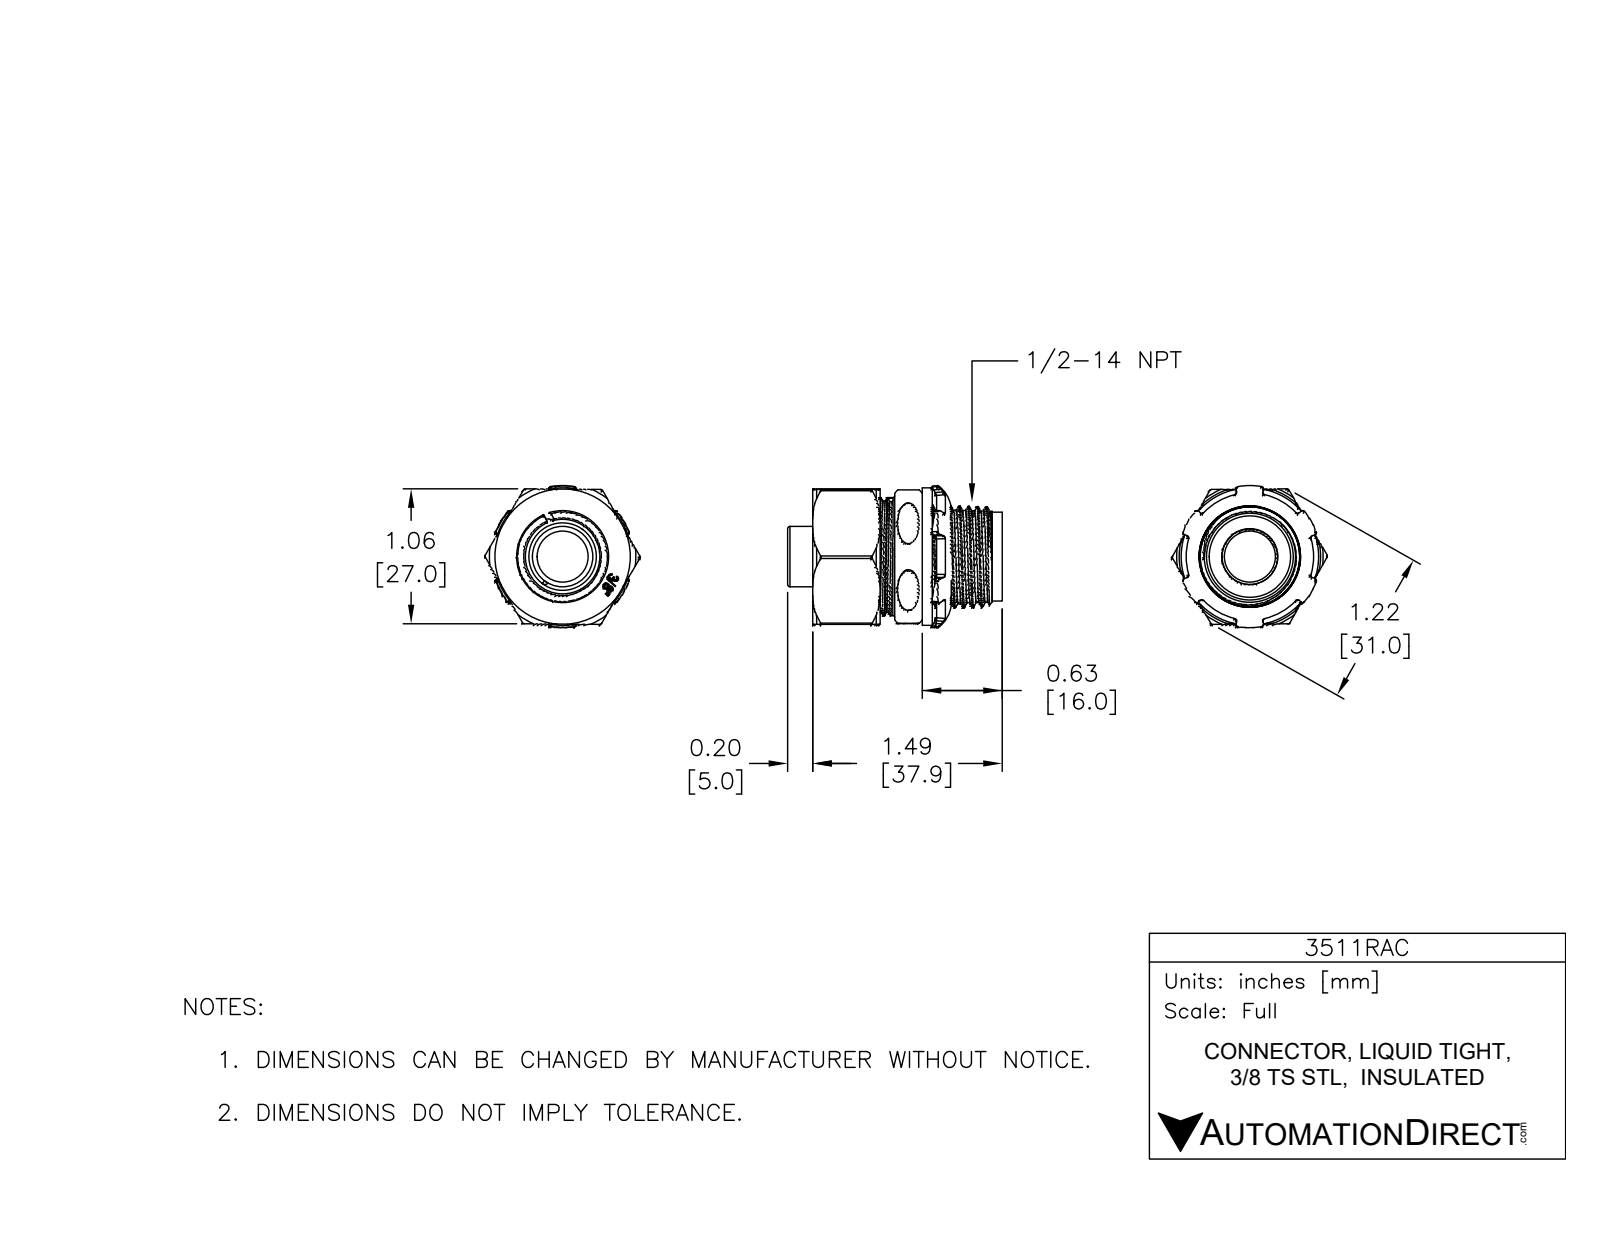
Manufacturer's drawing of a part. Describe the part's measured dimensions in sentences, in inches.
The part is named "3511RAC; 3511RAC-4; 3511RAC-2; 3511RAC-5 (+4 more)". Its 3-D file was written by "SolidWorks 2017 (AUTOMOTIVE_DESIGN)". It is 7 solids with 656 faces: 222 planar, 102 cylindrical and 332 other. Overall it measures 1.695 by 1.221 by 1.119 inches. Its volume is 0.549 cubic inches and its surface area 23.43 square inches. Round holes: 1 of diameter 0.1, 1 of diameter 0.402, 1 of diameter 0.44, 1 of diameter 0.567, 1 of diameter 0.728, 1 of diameter 0.732, 1 of diameter 0.787, 1 of diameter 0.858, 1 of diameter 0.906. Round bosses or shafts: 1 of diameter 1.083, 1 of diameter 0.93, 1 of diameter 0.866, 1 of diameter 0.768, 1 of diameter 0.701, 1 of diameter 0.641, 1 of diameter 0.476, 1 of diameter 0.438. Partial cylindrical surfaces (rounded edges, fillets, slot ends): 8 of radius 0.006, 6 of radius 0.02, 2 of radius 0.034, 1 of radius 0.008, 1 of radius 0.013, 1 of radius 0.334. The main face-to-face distances are 1.063, 0.863, 0.942, 0.079, 1.063, 0.531, 0.332, 0.411, 1.497, 0.966. The hole center spacings are 0.453.
